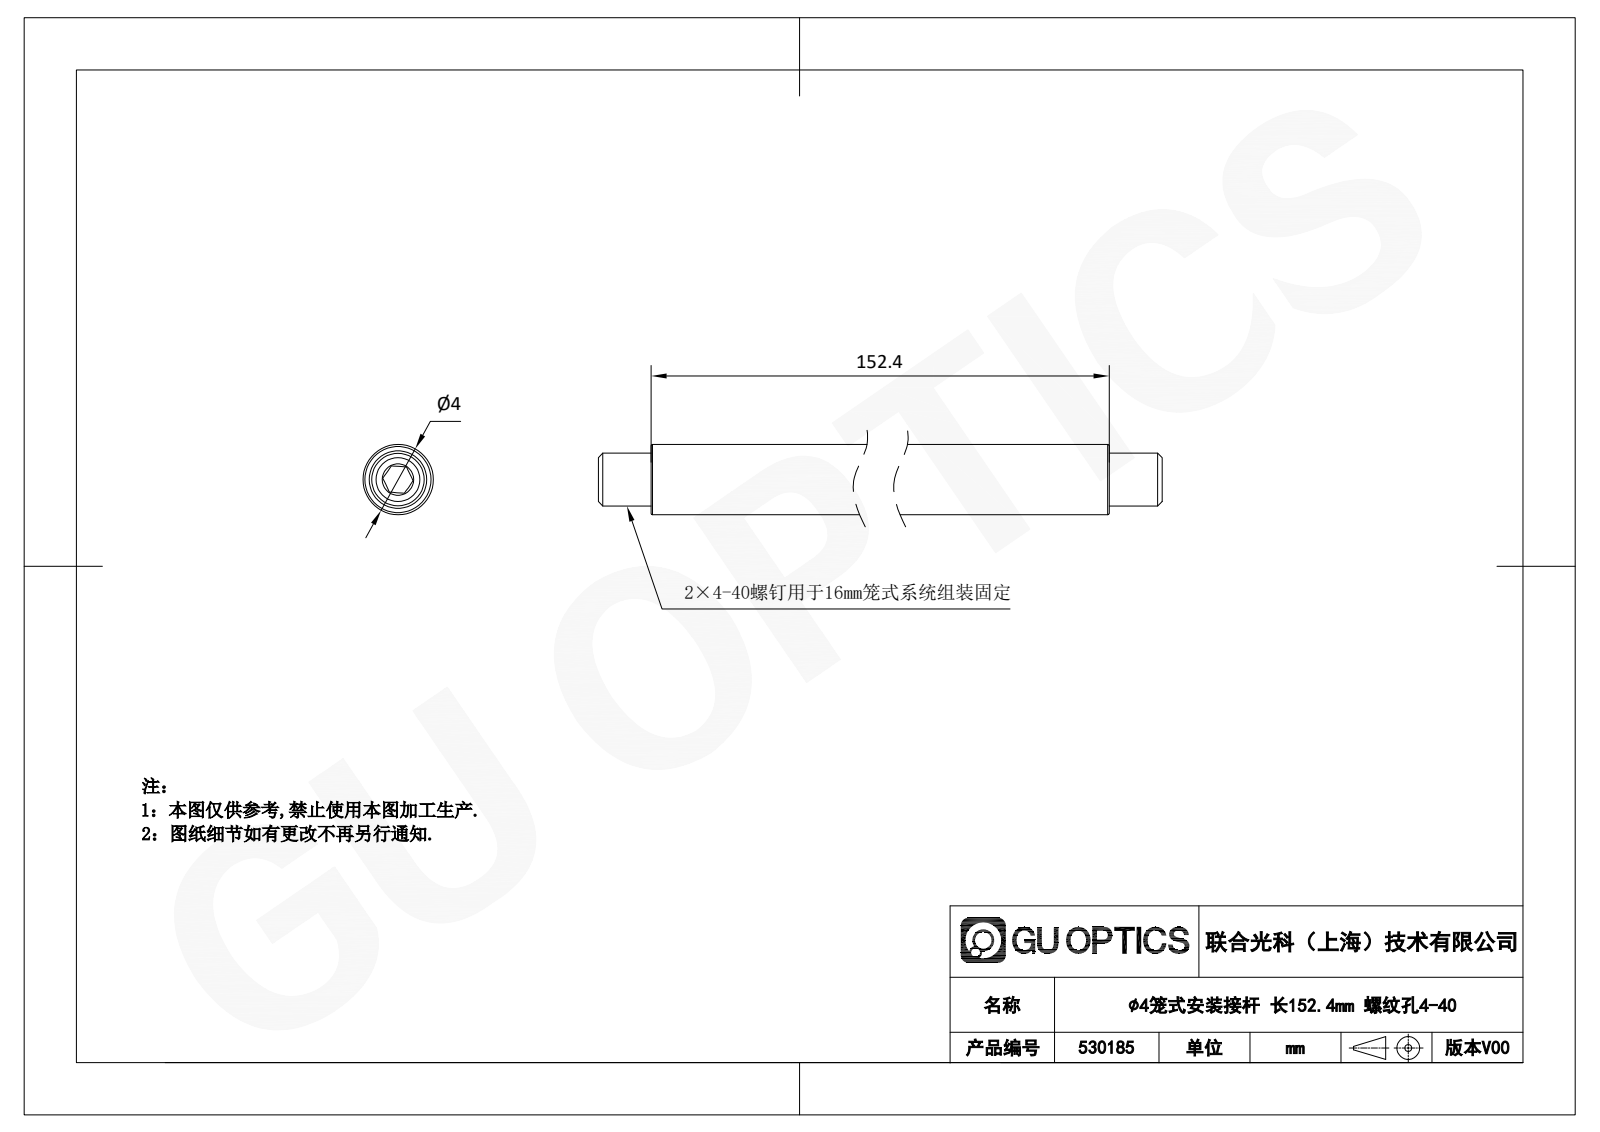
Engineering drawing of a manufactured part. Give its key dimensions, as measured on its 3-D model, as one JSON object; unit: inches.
{"part_name": "530185", "step_written_by": "SolidWorks 2020 (CONFIG_CONTROL_DESIGN)", "units": "inches", "bodies": {"solids": 3, "faces": 37, "planar": 20, "cylindrical": 5, "other": 12}, "overall_size": [6.394, 0.157, 0.157], "volume_in3": 0.12, "surface_area_in2": 3.418, "round_holes": [[0.098, 1]], "round_bosses_or_shafts": [[0.157, 1], [0.118, 1]], "face_to_face_distances": [0.118, 5.882, 0.197, 0.315, 6.079, 6.197, 0.059, 6, 0.039, 6.354]}
